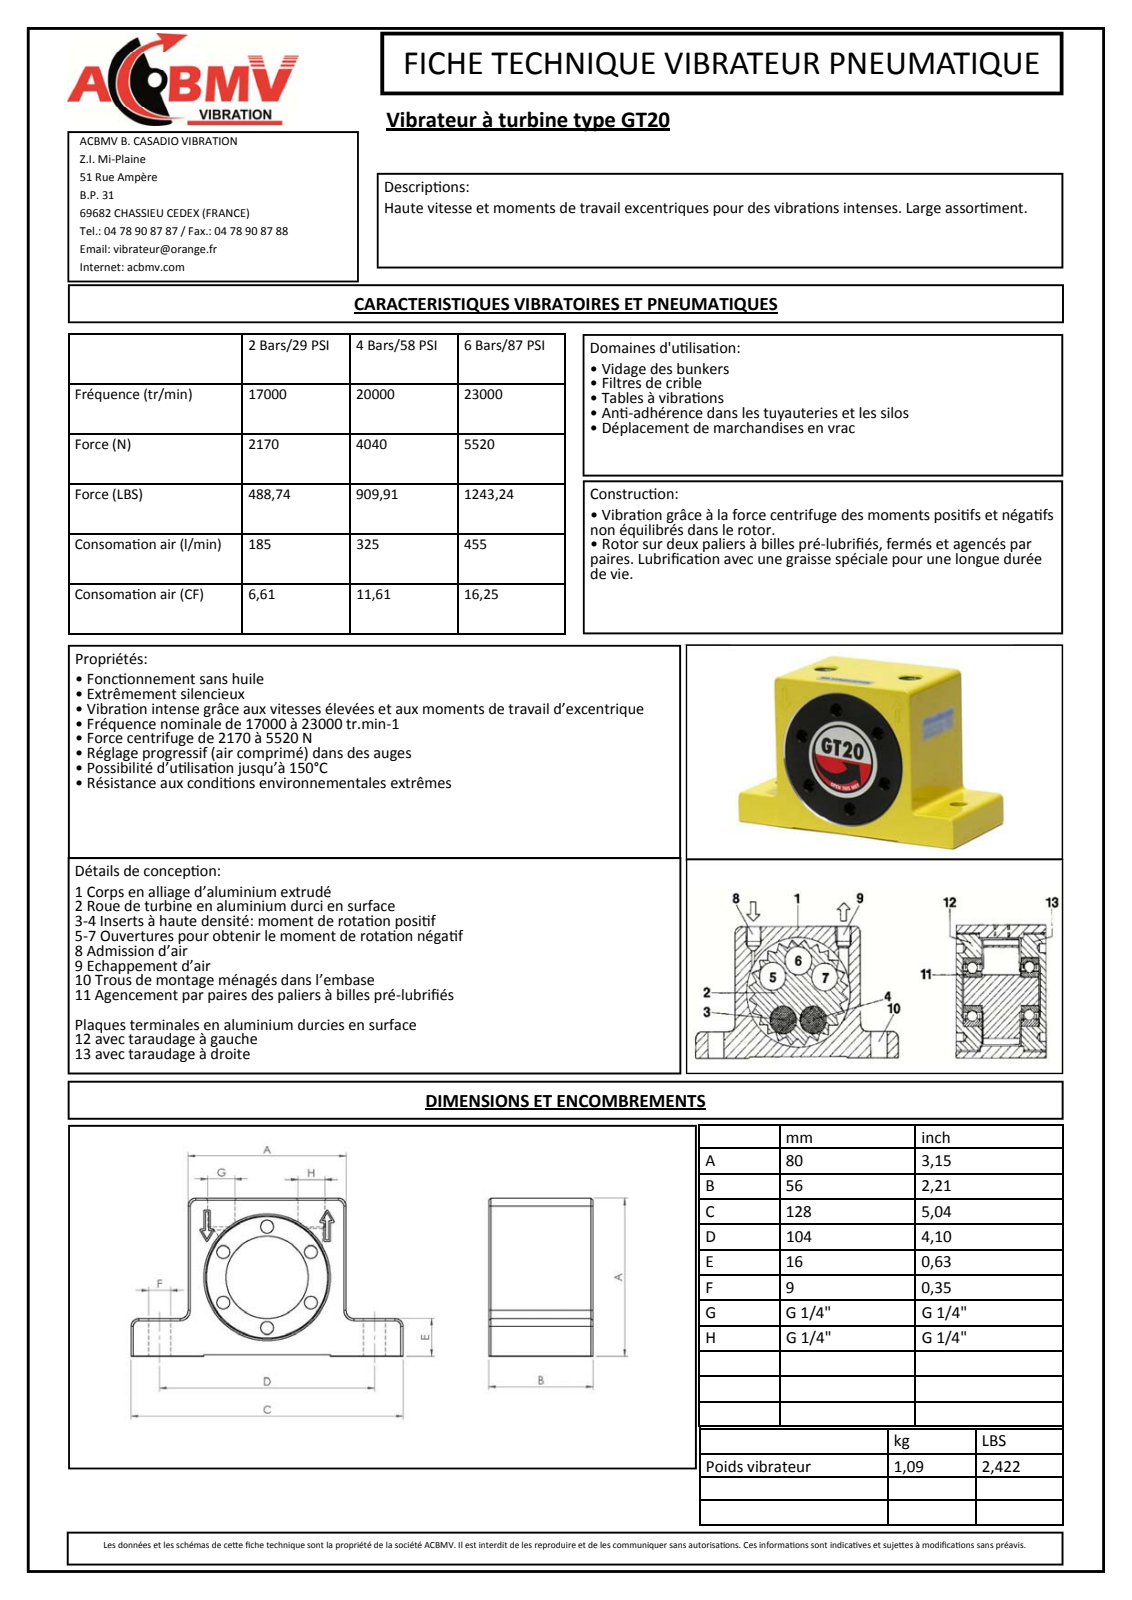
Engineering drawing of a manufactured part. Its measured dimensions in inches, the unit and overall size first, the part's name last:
Units: inches
Overall size (bounding box): 5.039 × 3.15 × 2.205
Round holes (diameter × count): ⌀0.236 ×6, ⌀0.354 ×4, ⌀0.451 ×2, ⌀0.117 ×1, ⌀1.614 ×1
Round bosses / shafts (diameter × count): ⌀0.106 ×1
Partial cylindrical surfaces — rounded edges, fillets, slot ends (radius × count): R0.01 ×14, R0.118 ×6, R0.03 ×4, R0.035 ×3, R0.041 ×3, R0.081 ×3, R0.015 ×2, R0.02 ×2
Main face-to-face distances: 3.15, 0.02, 2.193, 3.13, 2.205, 0.031, 2.173, 2.161, 2.181, 2.52
Hole centre spacings: 1.024, 1.773, 0.731, 1.063, 1.192, 1.67, 1.719, 1.773
Volume: 23.32 in³ · Surface area: 66.48 in²
Bodies: 1 solid, 277 faces (172 planar, 73 cylindrical, 32 other)
Part name (STEP PRODUCT): 8020-00-M
STEP written by: Autodesk Inventor 2011 (CONFIG_CONTROL_DESIGN)
